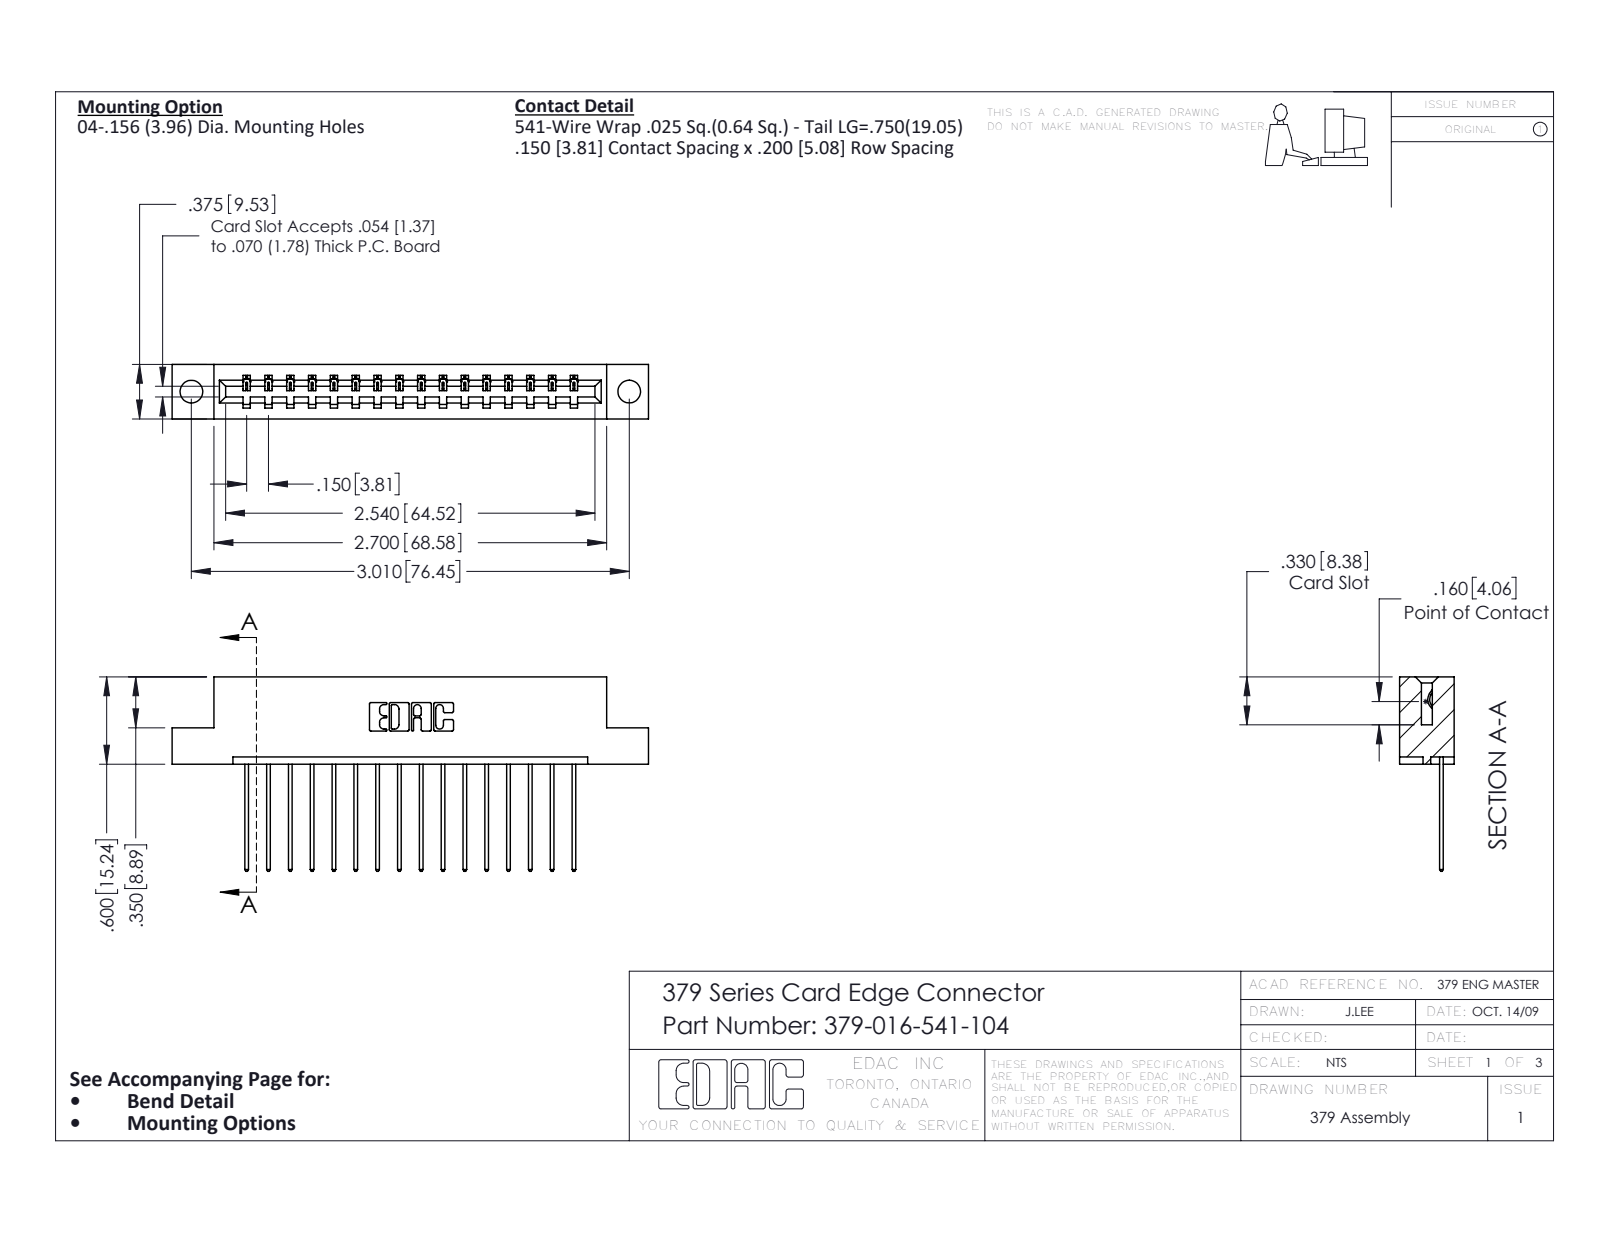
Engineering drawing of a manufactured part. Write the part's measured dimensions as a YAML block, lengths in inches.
part_name: "345-292-001_345-293-141; 379 Part_Flush - .156 Dia - TH; 379-016-541-104"
step_written_by: "SolidWorks 2020 (CONFIG_CONTROL_DESIGN)"
units: inches
bodies: {solids: 17, faces: 1042, planar: 742, cylindrical: 300, other: 0}
overall_size: [3.275, 1.337, 0.375]
volume: 0.512
surface_area: 13.3
round_holes:
  - {diameter: 0.156, count: 2}
partial_cylinders:
  - {radius: 0.006, count: 32}
  - {radius: 0.01, count: 32}
  - {radius: 0.01, count: 22}
  - {radius: 0.007, count: 6}
  - {radius: 0.031, count: 6}
  - {radius: 0.026, count: 3}
  - {radius: 0.014, count: 1}
  - {radius: 0.022, count: 1}
face_to_face_distances: [0.3, 0.075, 0.375, 0.6, 0.15, 0.225, 0.45, 0.2, 0.275, 0.1]
hole_center_spacings: [3.01]
